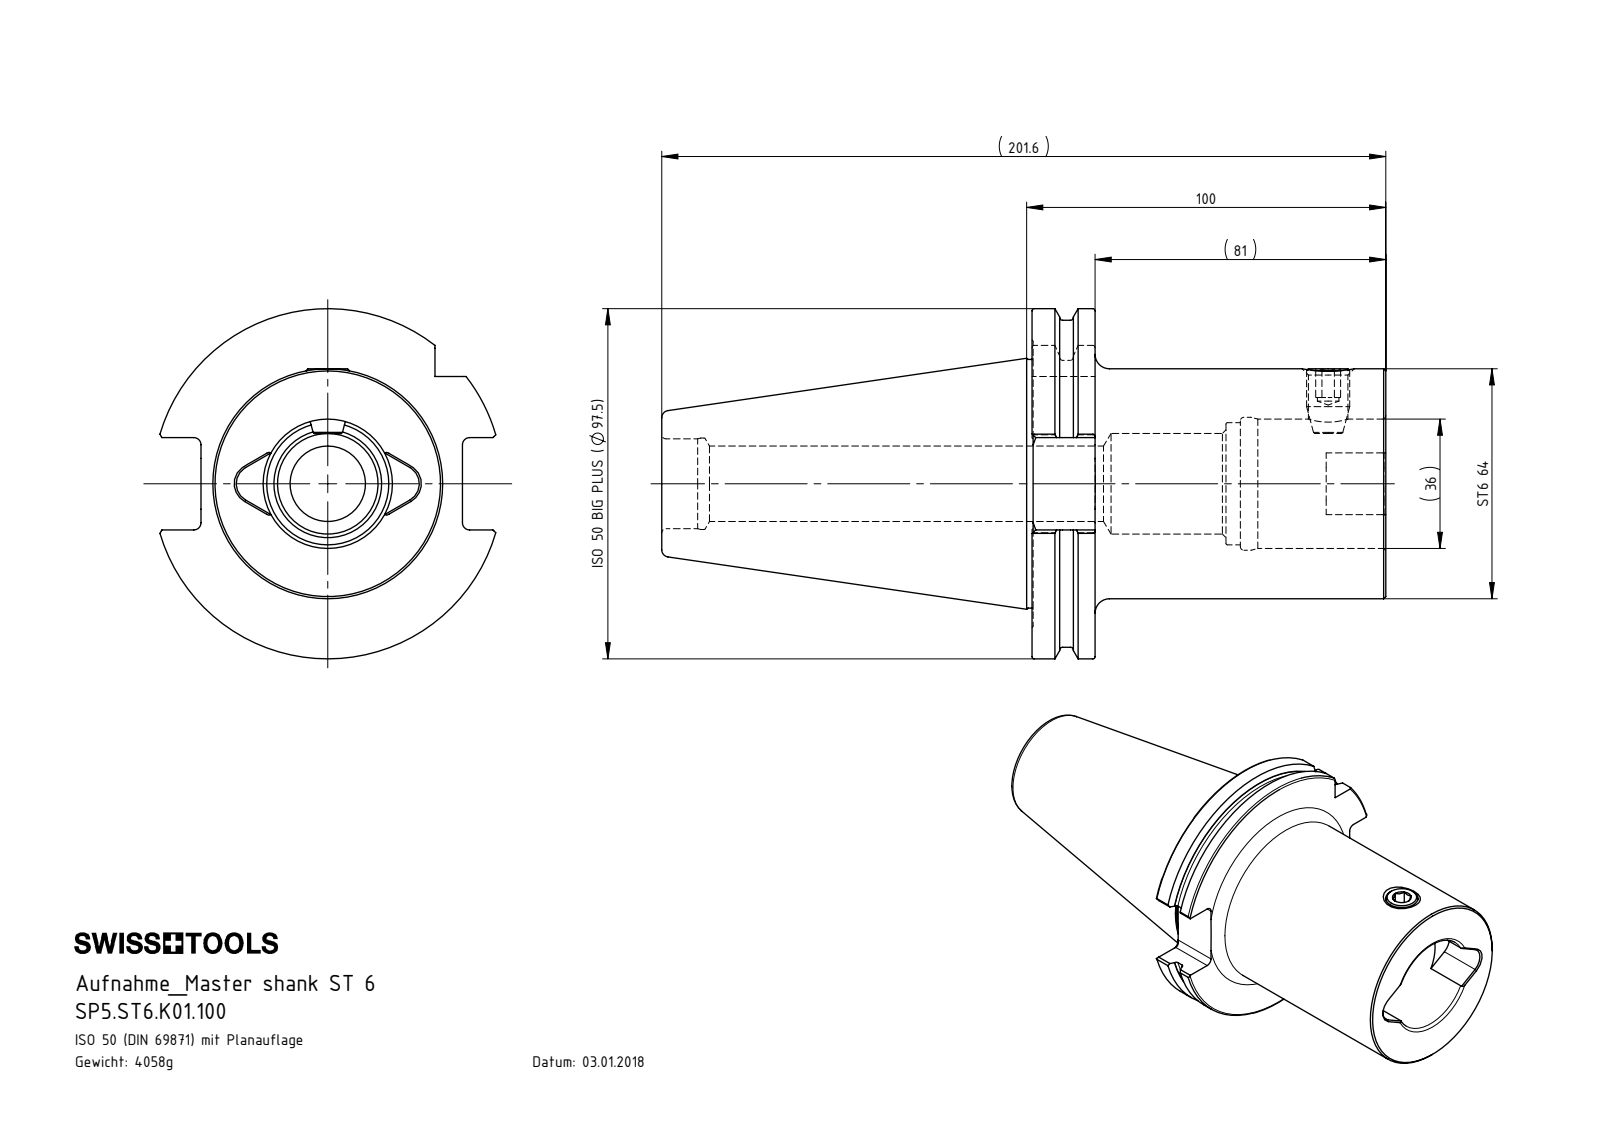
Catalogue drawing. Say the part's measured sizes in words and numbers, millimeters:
The part is named "SP5.ST6.K01.100; ST6-ER1.001.018_A; SP5-ST6.K01.100_B". Its 3-D file was written by "SolidWorks 2017 (AUTOMOTIVE_DESIGN)". It is 2 solids with 137 faces: 56 planar, 31 cylindrical and 50 other. Overall it measures 201.6 by 97.45 by 93.51 millimeters. Its volume is 516 889 cubic millimeters and its surface area 68 572 square millimeters. Round holes: 1 of diameter 6, 1 of diameter 11, 1 of diameter 21, 1 of diameter 25, 1 of diameter 25.45, 1 of diameter 28, 1 of diameter 34, 1 of diameter 36, 1 of diameter 37. Round bosses or shafts: 1 of diameter 91, 1 of diameter 69.2, 1 of diameter 64, 1 of diameter 12. Partial cylindrical surfaces (rounded edges, fillets, slot ends): 4 of radius 1.9, 4 of radius 2, 2 of radius 5.2, 1 of radius 48.73. The main face-to-face distances are 80.95, 17.55, 98.5, 17.25, 98.2, 103.1, 103.4, 120.65, 201.6, 72.8.
